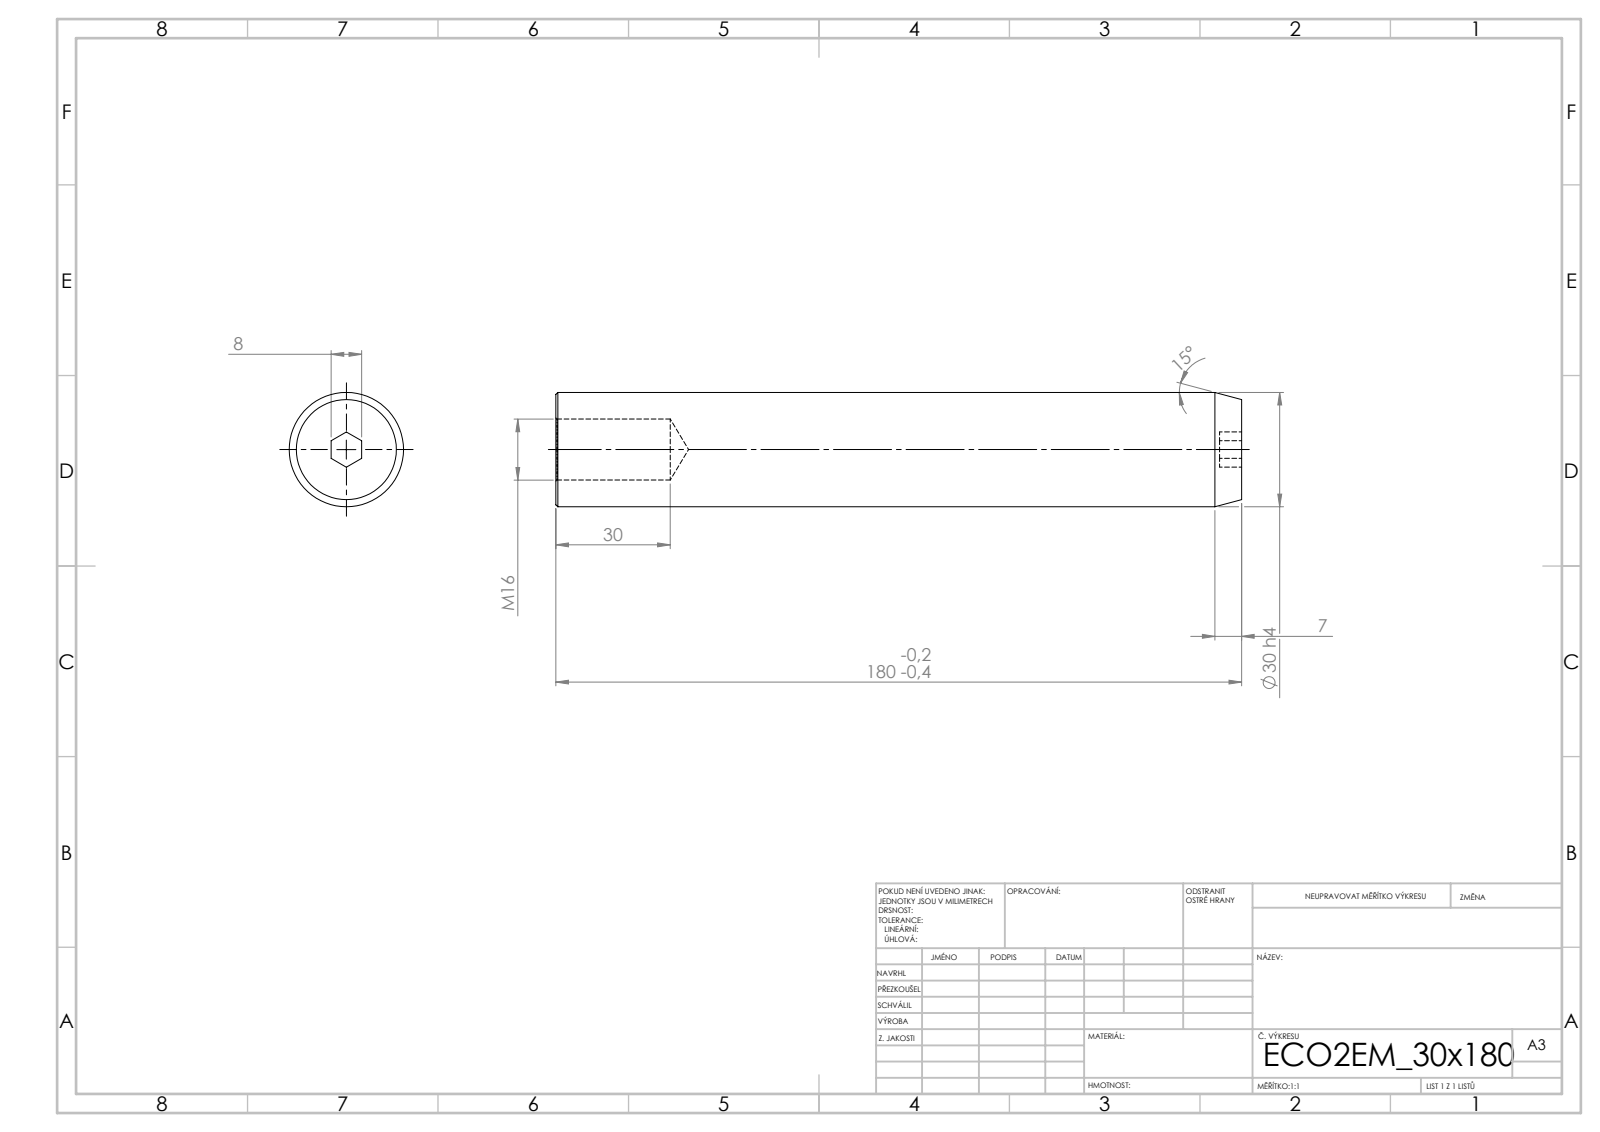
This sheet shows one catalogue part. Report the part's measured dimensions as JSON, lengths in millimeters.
{"step_written_by": "SolidWorks 2019 (CONFIG_CONTROL_DESIGN)", "units": "millimeters", "bodies": {"solids": 1, "faces": 21, "planar": 9, "cylindrical": 4, "other": 8}, "overall_size": [180, 30, 30], "volume_mm3": 119953, "surface_area_mm2": 19861, "round_holes": [[16, 1]], "round_bosses_or_shafts": [[30, 1]], "face_to_face_distances": [180, 8, 5.8, 174.2]}
